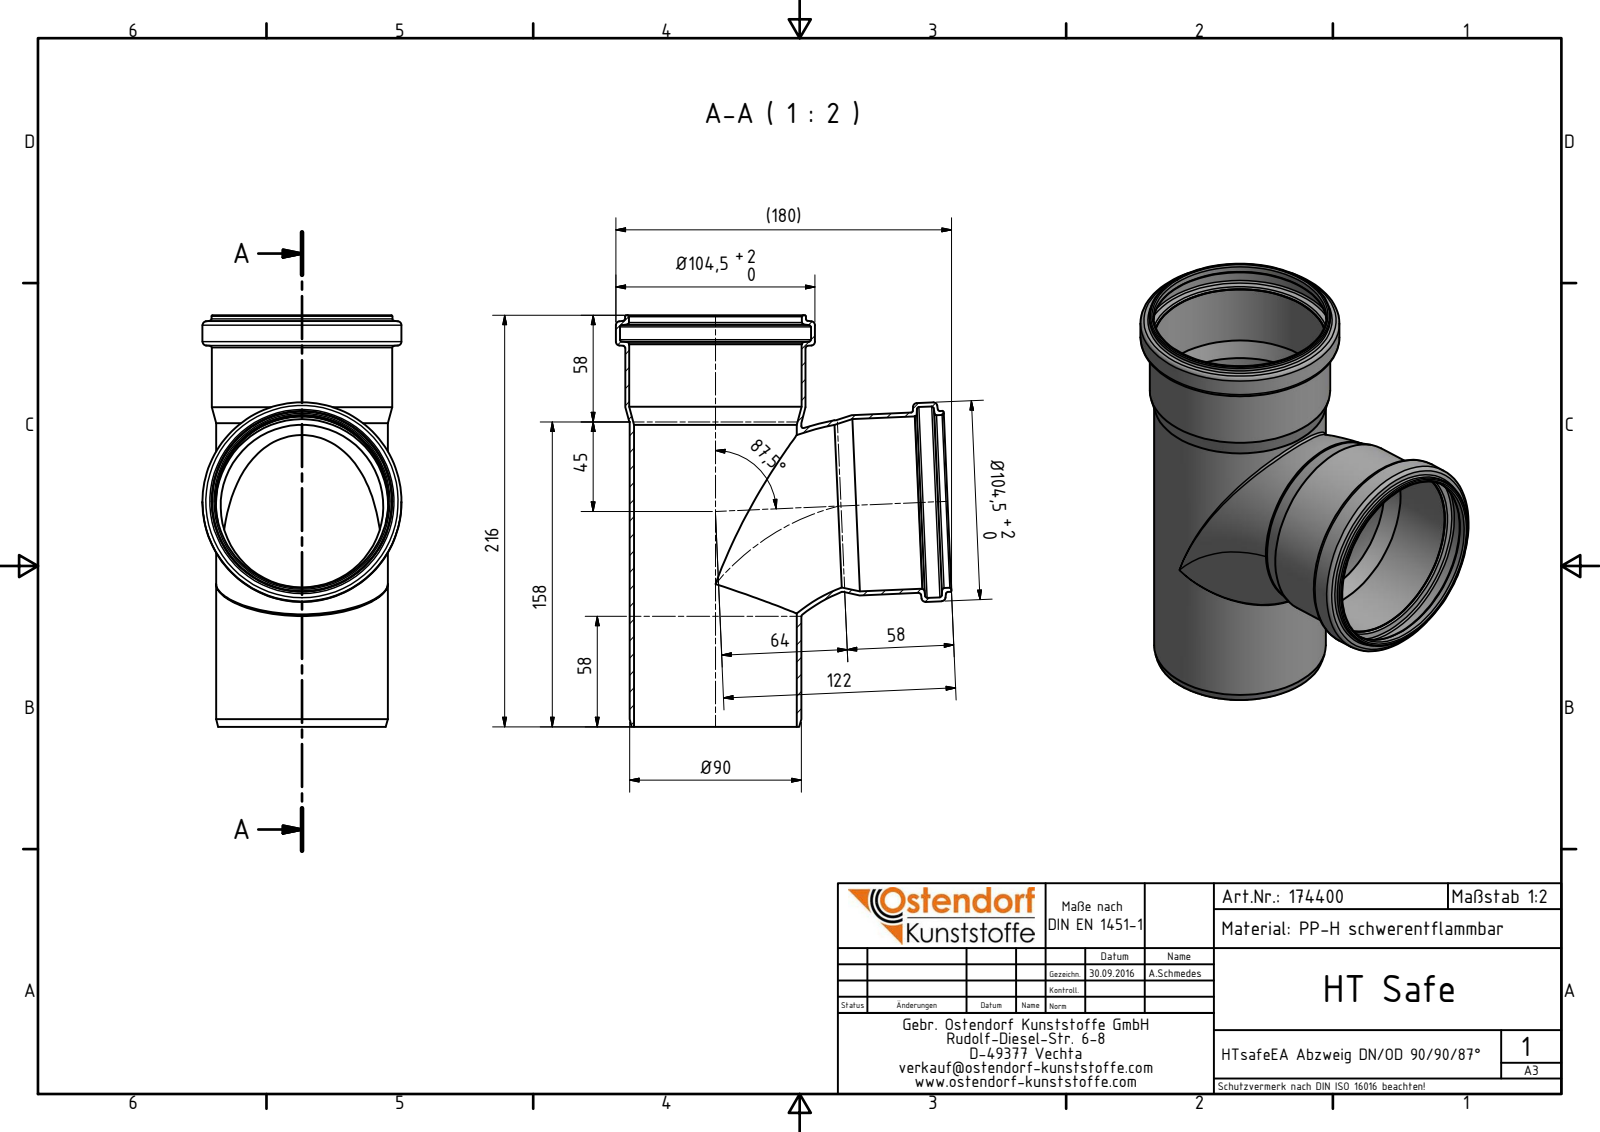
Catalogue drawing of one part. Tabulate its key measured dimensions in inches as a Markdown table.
| quantity | value |
| --- | --- |
| part name | 174400 HTsafeEA DN_OD 90_90_87° |
| STEP written by | Autodesk Inventor 2016 (AUTOMOTIVE_DESIGN) |
| units | inches |
| bodies | 1 solid, 59 faces (5 planar, 17 cylindrical, 37 other) |
| overall size | 8.504 × 6.936 × 4.114 |
| volume | 11.71 in³ |
| surface area | 264.2 in² |
| round holes (diameter × count) | 3.563 × 2, 3.575 × 2, 3.949 × 2, 3.362 × 1 |
| round bosses / shafts (diameter × count) | 4.114 × 2, 3.74 × 2, 3.728 × 2, 3.551 × 2 |
| main face-to-face distances | 8.504, 0.599, 7.905 |
